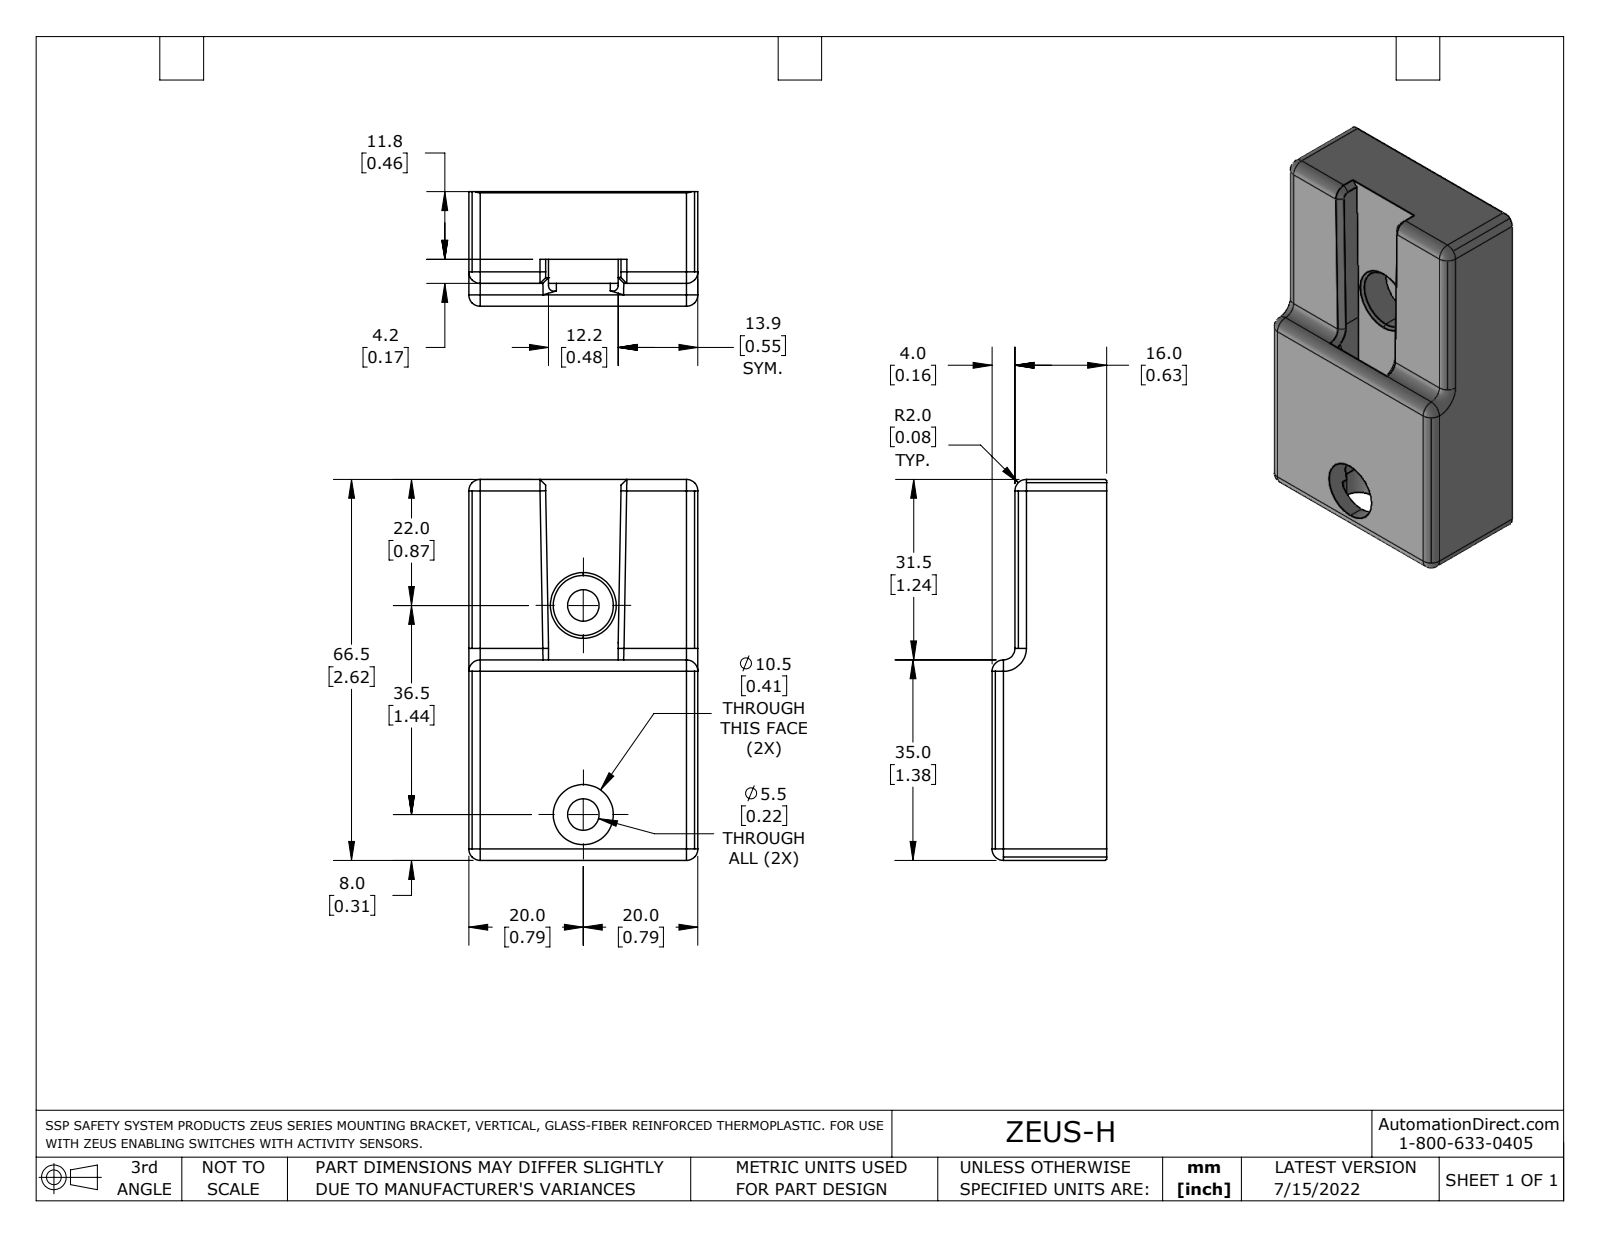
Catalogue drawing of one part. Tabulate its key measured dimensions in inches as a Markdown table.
| quantity | value |
| --- | --- |
| part name | ZEUS-H |
| STEP written by | SolidWorks 2021 (AUTOMOTIVE_DESIGN) |
| units | inches |
| bodies | 1 solid, 98 faces (34 planar, 40 cylindrical, 24 other) |
| overall size | 2.618 × 1.575 × 0.787 |
| volume | 2.56 in³ |
| surface area | 16.98 in² |
| round holes (diameter × count) | 0.217 × 2, 0.413 × 2, 0.317 × 1 |
| partial cylindrical surfaces (radius × count) | 0.079 × 12, 0.118 × 4, 0.055 × 2 |
| main face-to-face distances | 0.787, 1.575, 0.157, 0.63, 0.323, 0.165, 0.465, 2.618, 0.547, 1.028 |
| hole center spacings | 0.689, 1.437, 2.126 |
